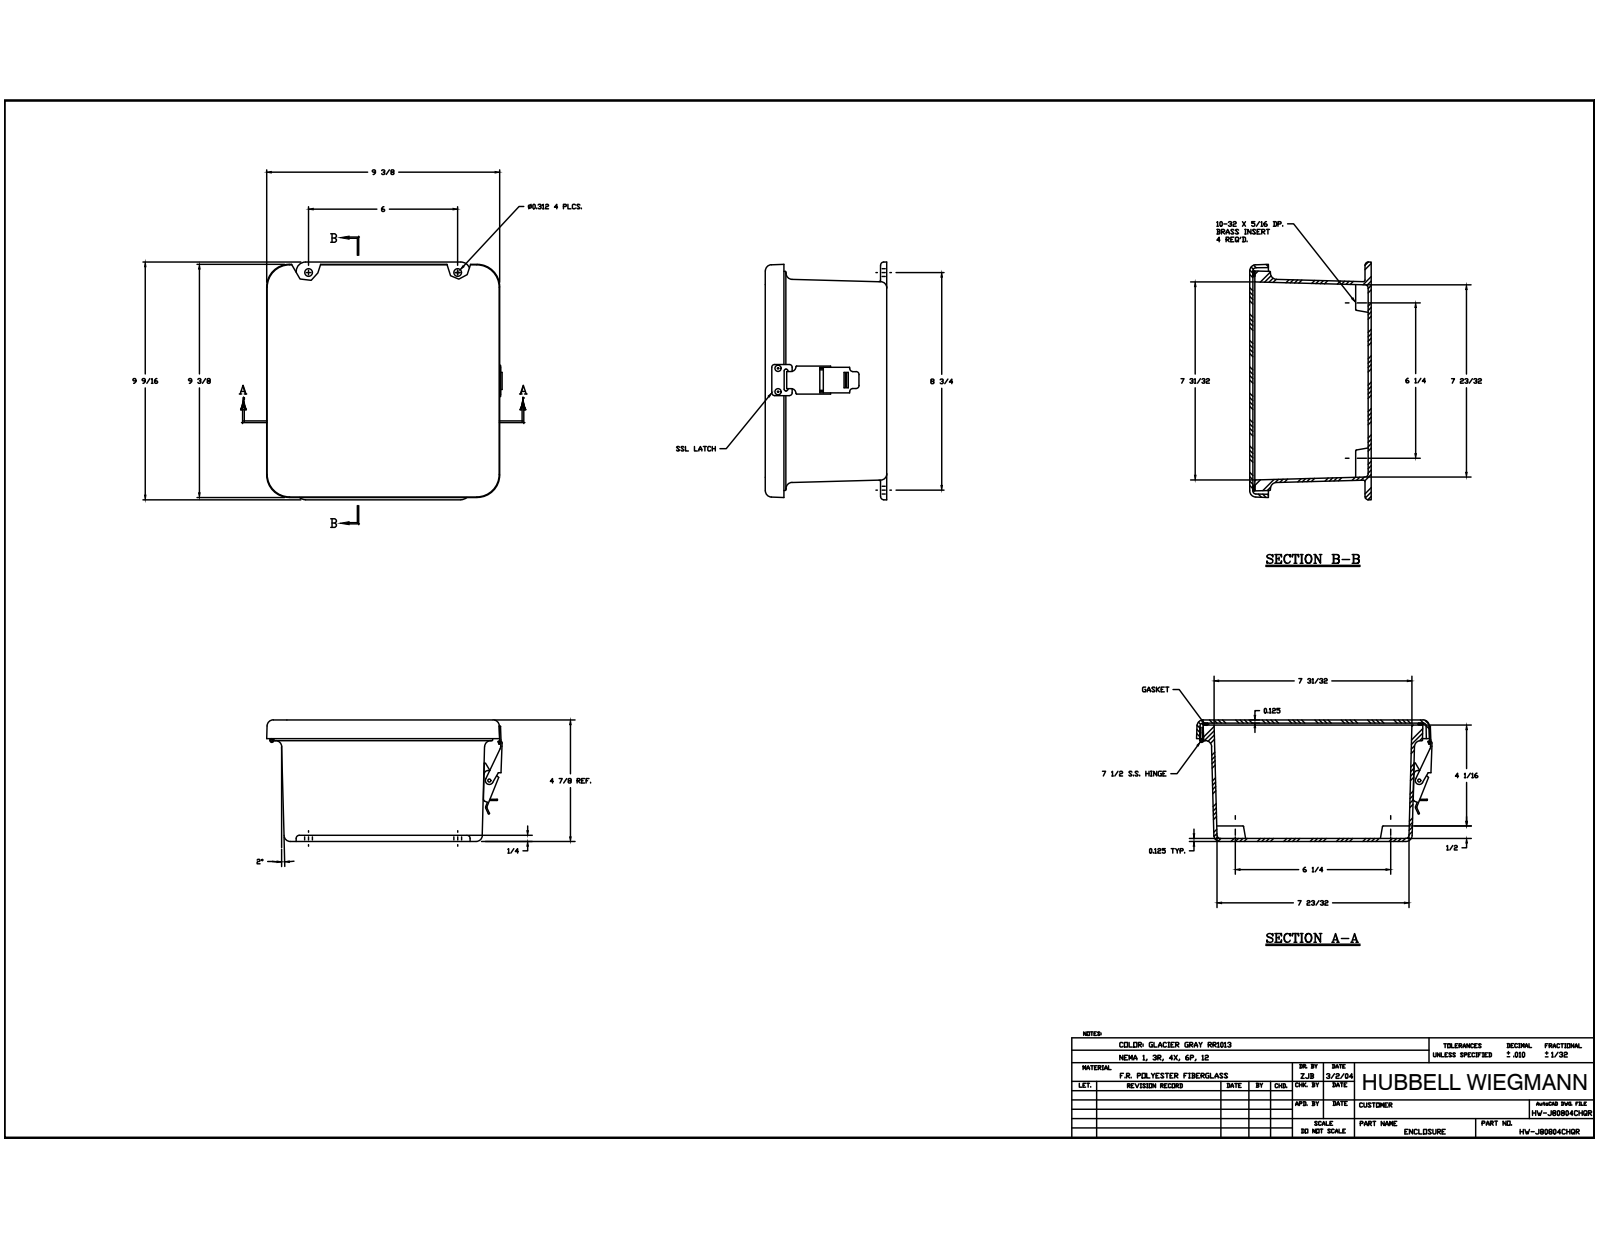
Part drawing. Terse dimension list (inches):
name: J808HL_2; RMINS45821P_17; RMINS45821P_18; RMINS45821P_19 (+8 more)
written by: Autodesk Inventor 2014 (AUTOMOTIVE_DESIGN)
unit: in
bodies: 26 solids, 779 faces (293 planar, 313 cylindrical, 173 other)
size: 9.561 × 9.533 × 4.888
volume: 51.78 in³; area: 751.2 in²
holes: 12× ⌀0.14, 8× ⌀0.152, 6× ⌀0.131, 4× ⌀0.104, 4× ⌀0.156, 4× ⌀0.218, 2× ⌀0.13, 2× ⌀0.135, 1× ⌀0.085, 1× ⌀0.375
bosses: 10× ⌀0.125, 6× ⌀0.25, 4× ⌀0.27, 1× ⌀0.3, 1× ⌀0.17, 1× ⌀0.155, 1× ⌀0.12
rounds: 36× R0.031, 16× R0.125, 12× R0.015, 12× R0.25, 8× R0.045, 7× R0.2, 6× R0.03, 5× R0.022
face distances: 0.125, 4.763, 4.888, 4.638, 0.125, 4.763, 4.56, 0.203, 0.078, 4.685
hole spacings: 3.5, 7.249, 0.937, 8.125, 10.165, 0.25, 0.75, 3.25
